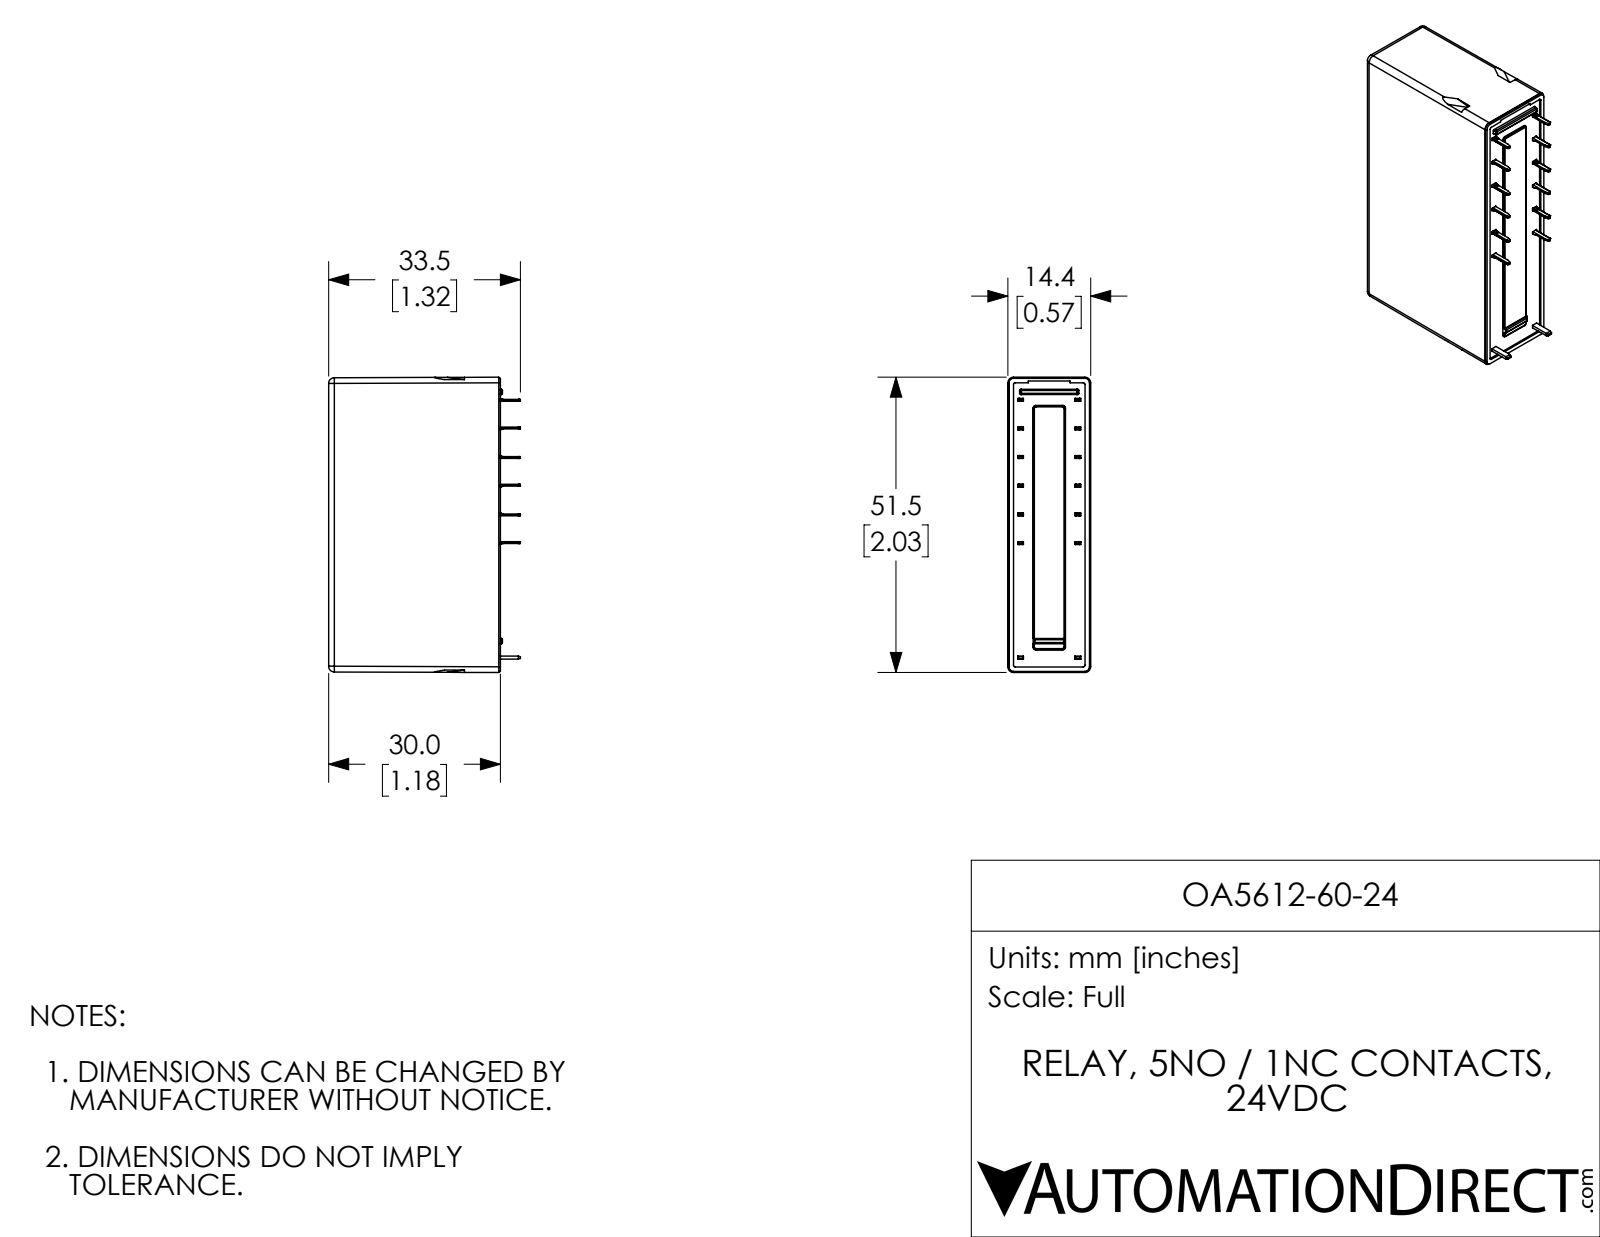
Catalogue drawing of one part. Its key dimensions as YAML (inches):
part_name: "OA5612-60-24"
step_written_by: "SolidWorks 2017 (AUTOMOTIVE_DESIGN)"
units: inches
bodies: {solids: 1, faces: 434, planar: 262, cylindrical: 126, other: 46}
overall_size: [2.029, 1.319, 0.569]
volume: 1.342
surface_area: 8.543
round_bosses_or_shafts:
  - {diameter: 0.031, count: 1}
partial_cylinders:
  - {radius: 0.006, count: 36}
  - {radius: 0.008, count: 16}
  - {radius: 0.02, count: 16}
  - {radius: 0.039, count: 8}
  - {radius: 0.012, count: 4}
  - {radius: 0.005, count: 2}
  - {radius: 0.01, count: 2}
face_to_face_distances: [1.169, 1.181, 0.394, 0.016, 0.427, 0.19, 0.013, 0.492, 0.065, 0.035]
